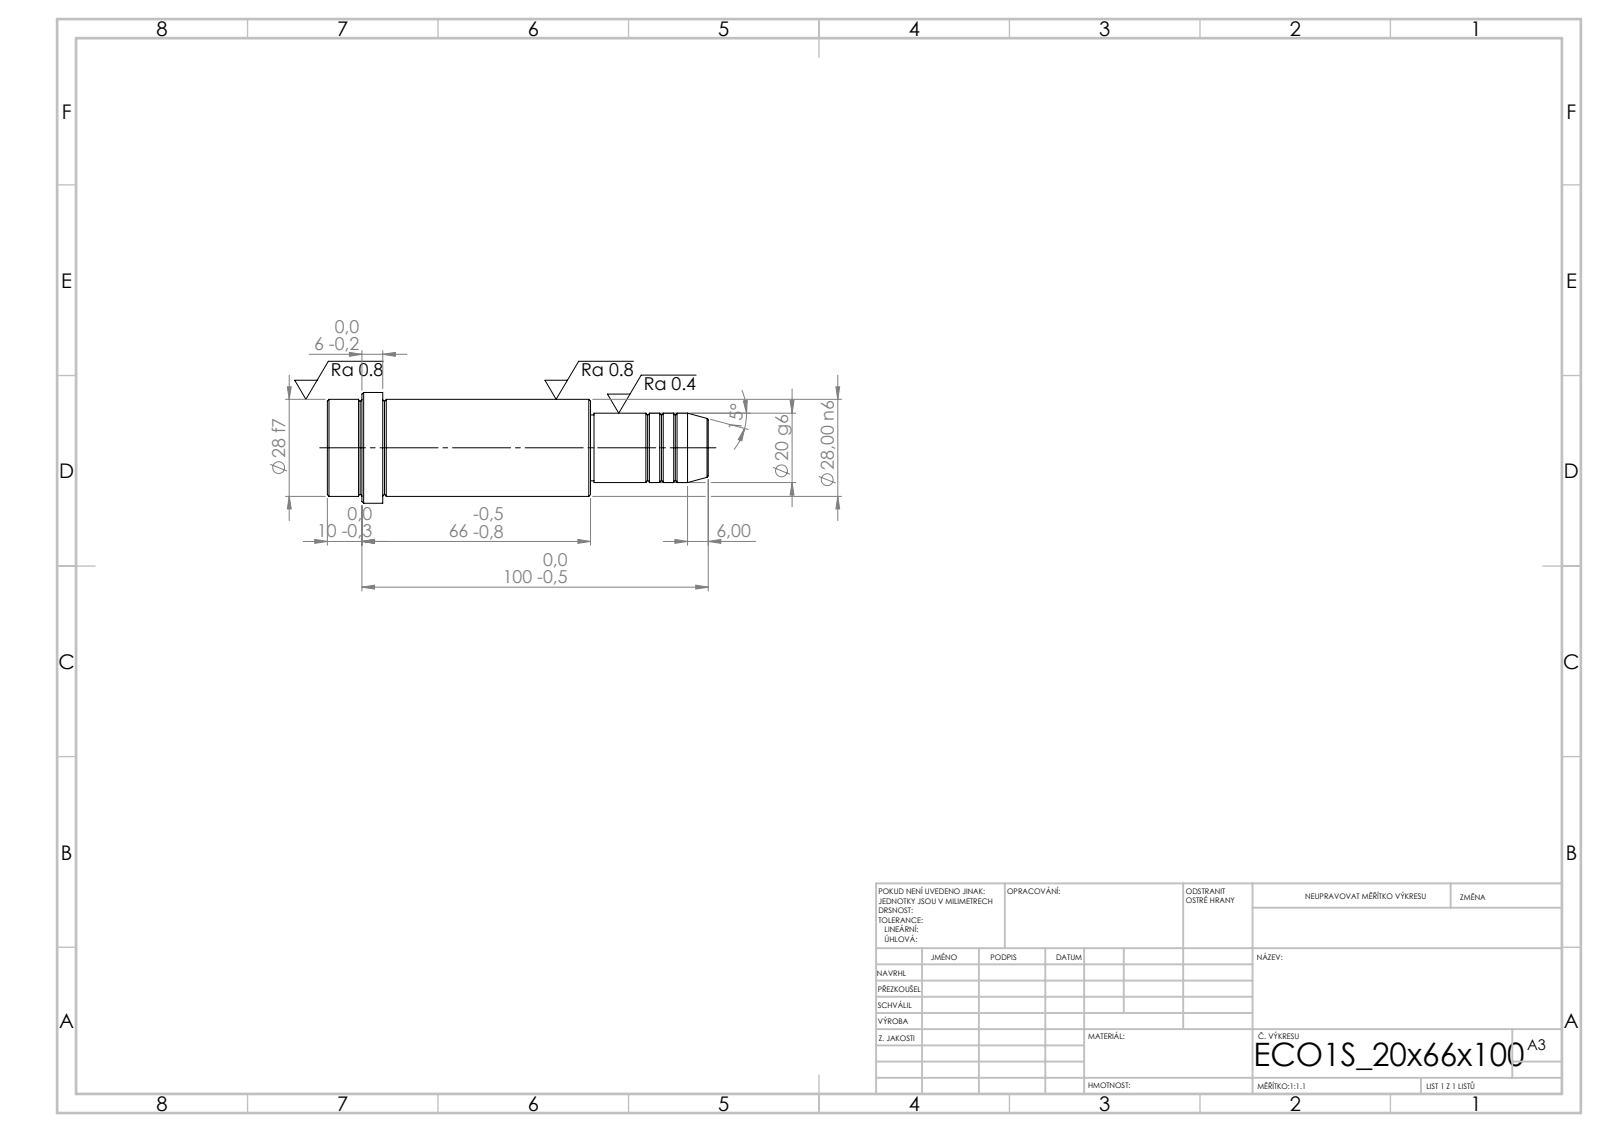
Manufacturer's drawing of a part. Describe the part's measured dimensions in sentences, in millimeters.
Its 3-D file was written by "SolidWorks 2019 (CONFIG_CONTROL_DESIGN)". It is 1 solid with 52 faces: 6 planar, 16 cylindrical and 30 other. Overall it measures 110 by 32 by 32 millimeters. Its volume is 58 116 cubic millimeters and its surface area 10 557 square millimeters. Round bosses or shafts: 1 of diameter 32, 1 of diameter 28, 1 of diameter 20, 1 of diameter 19. The main face-to-face distances are 76, 34, 110, 94, 60, 16, 100, 66, 6, 10.
